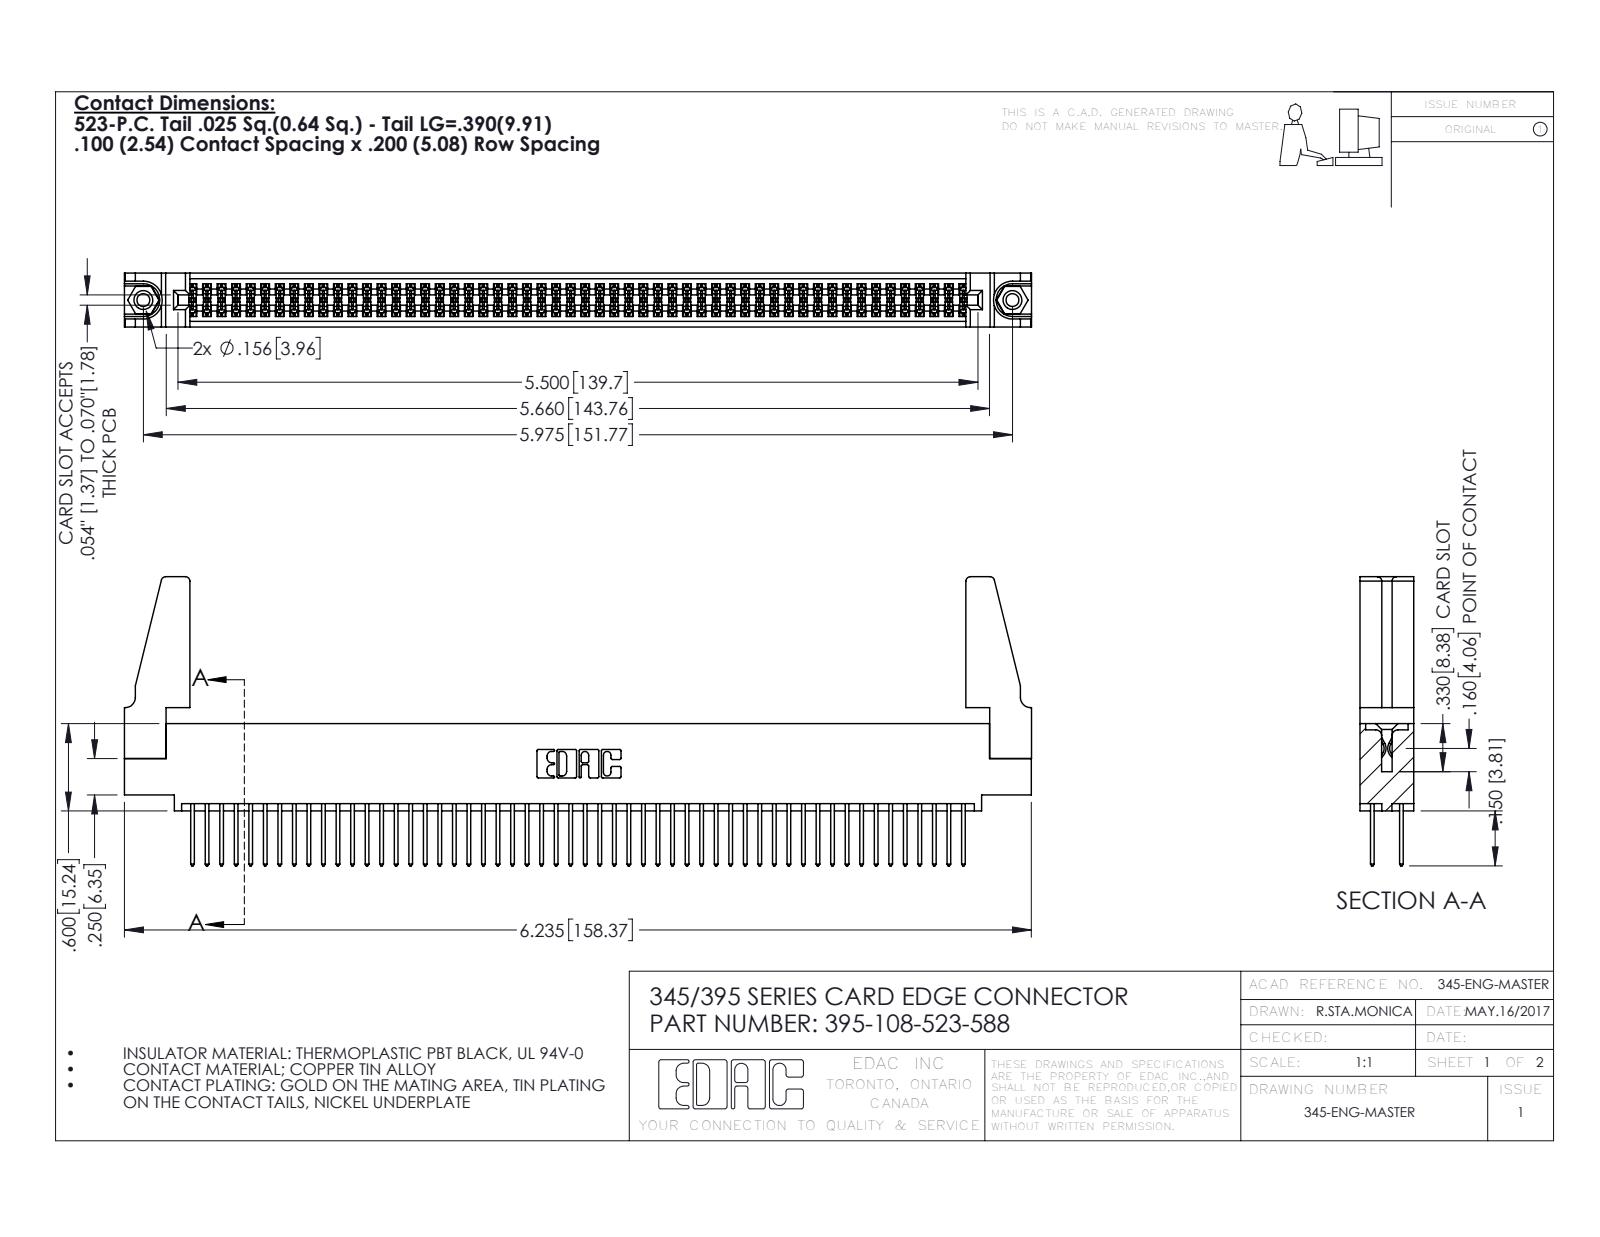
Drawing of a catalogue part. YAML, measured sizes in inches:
part_name: "395-108-523-588; 345-220-078_345-220-088; 345-292-001_345-293-123; 345-250-001_345-250-001-102 (+1 more)"
step_written_by: "SolidWorks 2016 (CONFIG_CONTROL_DESIGN)"
units: inches
bodies: {solids: 113, faces: 5654, planar: 3720, cylindrical: 1918, other: 16}
overall_size: [6.236, 1.987, 0.37]
volume: 1.153
surface_area: 42.73
round_holes:
  - {diameter: 0.089, count: 2}
  - {diameter: 0.125, count: 2}
  - {diameter: 0.156, count: 2}
  - {diameter: 0.064, count: 1}
round_bosses_or_shafts:
  - {diameter: 0.155, count: 2}
partial_cylinders:
  - {radius: 0.006, count: 162}
  - {radius: 0.01, count: 108}
  - {radius: 0.01, count: 22}
  - {radius: 0.03, count: 8}
  - {radius: 0.007, count: 6}
  - {radius: 0.031, count: 6}
  - {radius: 0.026, count: 3}
  - {radius: 0.014, count: 2}
face_to_face_distances: [0.072, 0.298, 0.37, 0.2, 0.098, 0.272, 0.025, 0.225, 0.175, 0.149]
hole_center_spacings: [0.27, 5.739, 5.975]
